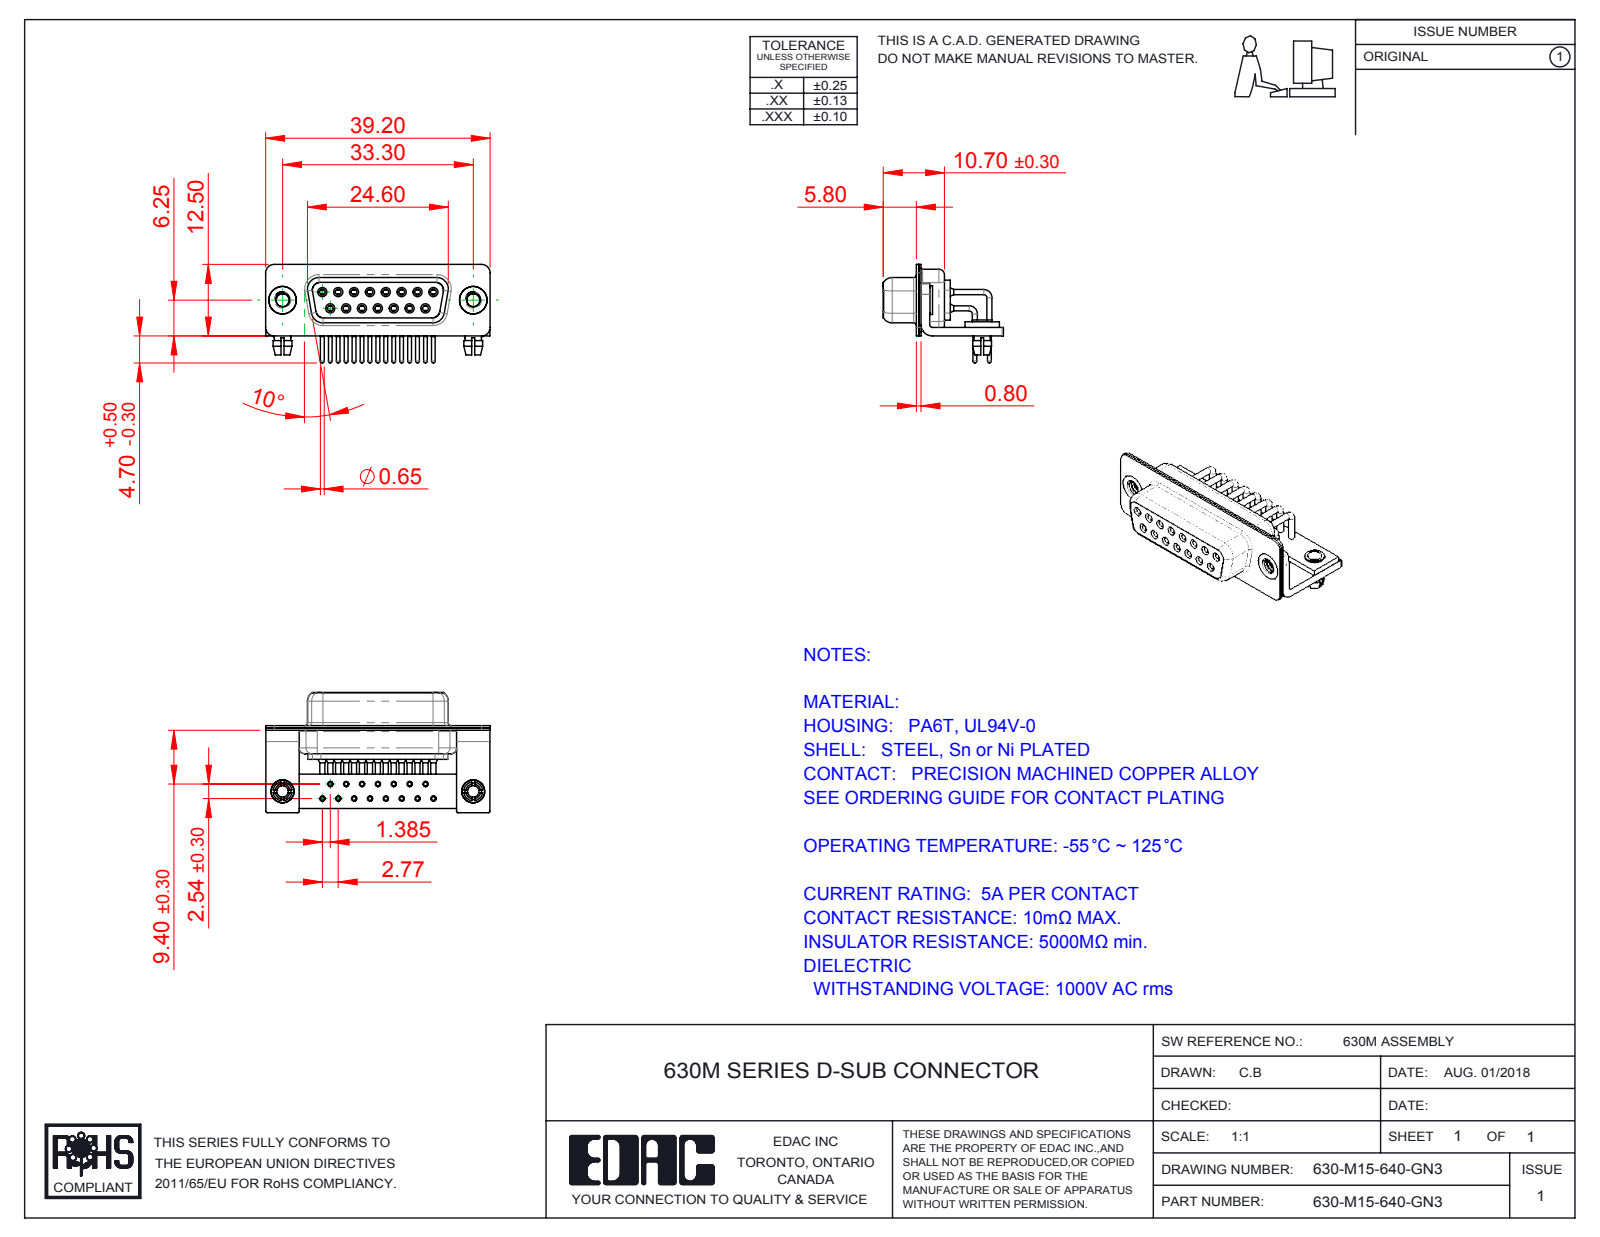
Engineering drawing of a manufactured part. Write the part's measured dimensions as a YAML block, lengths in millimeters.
part_name: "630M Shell Front_15 Contacts; 630M Contact Row 1; 630M Shell Rear_15 Contacts; 630M 4-40 Threaded Rivet_Stabilizer (+6 more)"
step_written_by: "SolidWorks 2016 (CONFIG_CONTROL_DESIGN)"
units: millimeters
bodies: {solids: 25, faces: 1246, planar: 366, cylindrical: 566, other: 314}
overall_size: [39.2, 21, 17.2]
volume: 3090
surface_area: 7958
round_holes:
  - {diameter: 2, count: 17}
  - {diameter: 0.9, count: 15}
  - {diameter: 1, count: 15}
  - {diameter: 1.1, count: 15}
  - {diameter: 1.7, count: 15}
  - {diameter: 1.8, count: 15}
  - {diameter: 2.26, count: 2}
  - {diameter: 2.5, count: 2}
  - {diameter: 3.2, count: 2}
  - {diameter: 4, count: 2}
  - {diameter: 4.8, count: 2}
round_bosses_or_shafts:
  - {diameter: 0.9, count: 27}
  - {diameter: 1.6, count: 15}
  - {diameter: 1.5, count: 15}
  - {diameter: 0.65, count: 15}
  - {diameter: 5, count: 2}
  - {diameter: 4.9, count: 2}
  - {diameter: 4, count: 2}
  - {diameter: 3.4, count: 2}
partial_cylinders:
  - {radius: 0.25, count: 16}
  - {radius: 1.5, count: 16}
  - {radius: 2, count: 13}
  - {radius: 1.35, count: 8}
  - {radius: 1.6, count: 8}
  - {radius: 0.5, count: 5}
  - {radius: 0.6, count: 4}
  - {radius: 0.65, count: 4}
face_to_face_distances: [0.4, 0.8, 2.3, 1.5, 9.35, 1.9, 1, 1.45, 8.95, 0.85]
hole_center_spacings: [2.77, 5.54, 8.31, 3.16, 4.87, 11.08, 2.89, 7.37]
